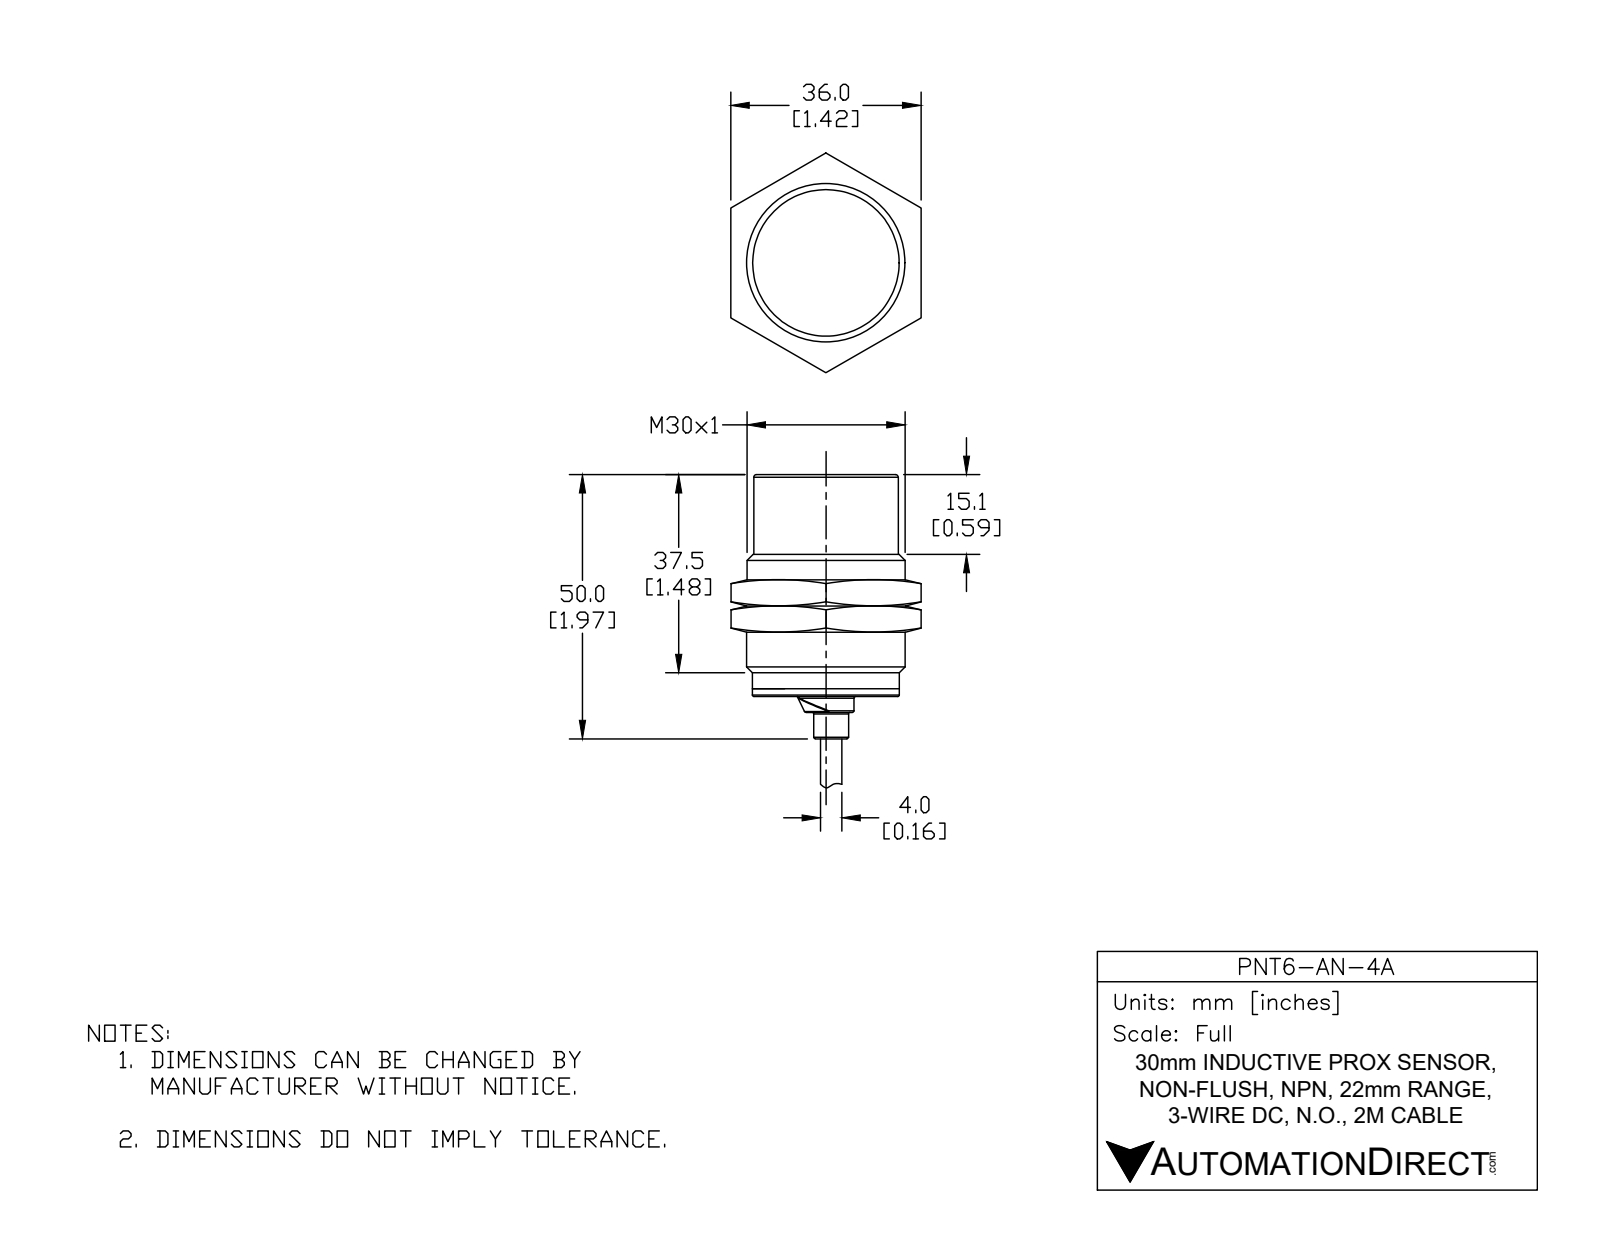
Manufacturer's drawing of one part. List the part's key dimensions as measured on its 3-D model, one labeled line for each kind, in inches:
Part name (STEP PRODUCT): PNT6-AN-4A
STEP written by: SolidWorks 2017 (AUTOMOTIVE_DESIGN)
Units: inches
Bodies: 1 solid, 77 faces (15 planar, 30 cylindrical, 32 other)
Overall size (bounding box): 3.969 × 1.181 × 1.181
Volume: 1.84 in³ · Surface area: 9.715 in²
Round holes (diameter × count): ⌀0.162 ×1
Round bosses / shafts (diameter × count): ⌀0.049 ×6, ⌀1.181 ×1, ⌀1.095 ×1, ⌀1.094 ×1, ⌀0.417 ×1, ⌀0.26 ×1, ⌀0.157 ×1
Partial cylindrical surfaces — rounded edges, fillets, slot ends (radius × count): R0.077 ×1
Main face-to-face distances: 1.654, 1.772, 0.118, 1.969, 0.315, 0.197, 3.969, 2.315, 2.197, 2
